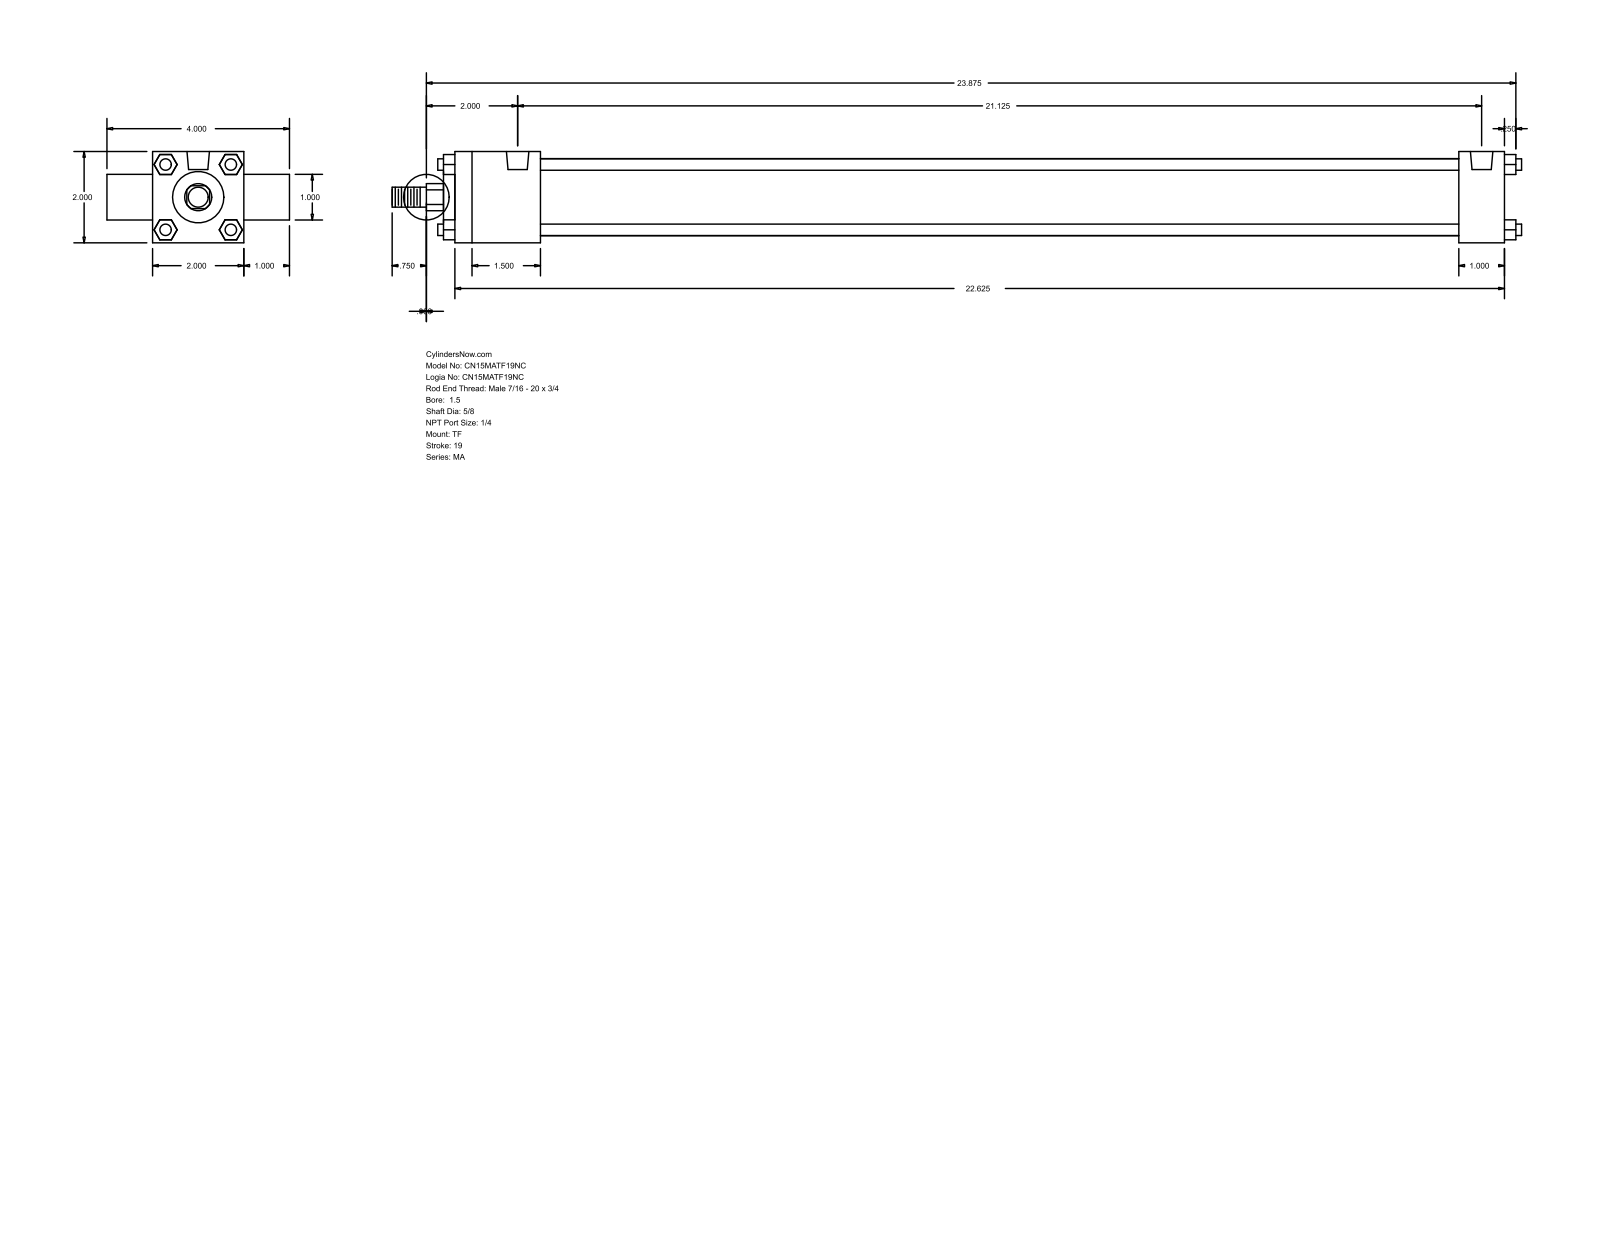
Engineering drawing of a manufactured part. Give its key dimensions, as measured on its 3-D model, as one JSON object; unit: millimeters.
{"part_name": "MA_TF__0150_0.625", "step_written_by": "GSSL Pune (CONFIG_CONTROL_DESIGN)", "units": "millimeters", "bodies": {"solids": 0, "faces": 120, "planar": 92, "cylindrical": 28, "other": 0}, "overall_size": [628.65, 101.6, 50.8], "round_holes": [[7.94, 3], [12.49, 2]], "round_bosses_or_shafts": [[6.35, 4], [42.93, 1], [28.57, 1], [25.4, 1], [15.88, 1], [11.11, 1]], "partial_cylinders_radius": [[7.54, 1]], "face_to_face_distances": [50.8, 584.2, 25.4, 76.2, 47.62, 558.79, 511.17, 536.58, 25.41, 6.35], "hole_center_spacings": [536.58]}
